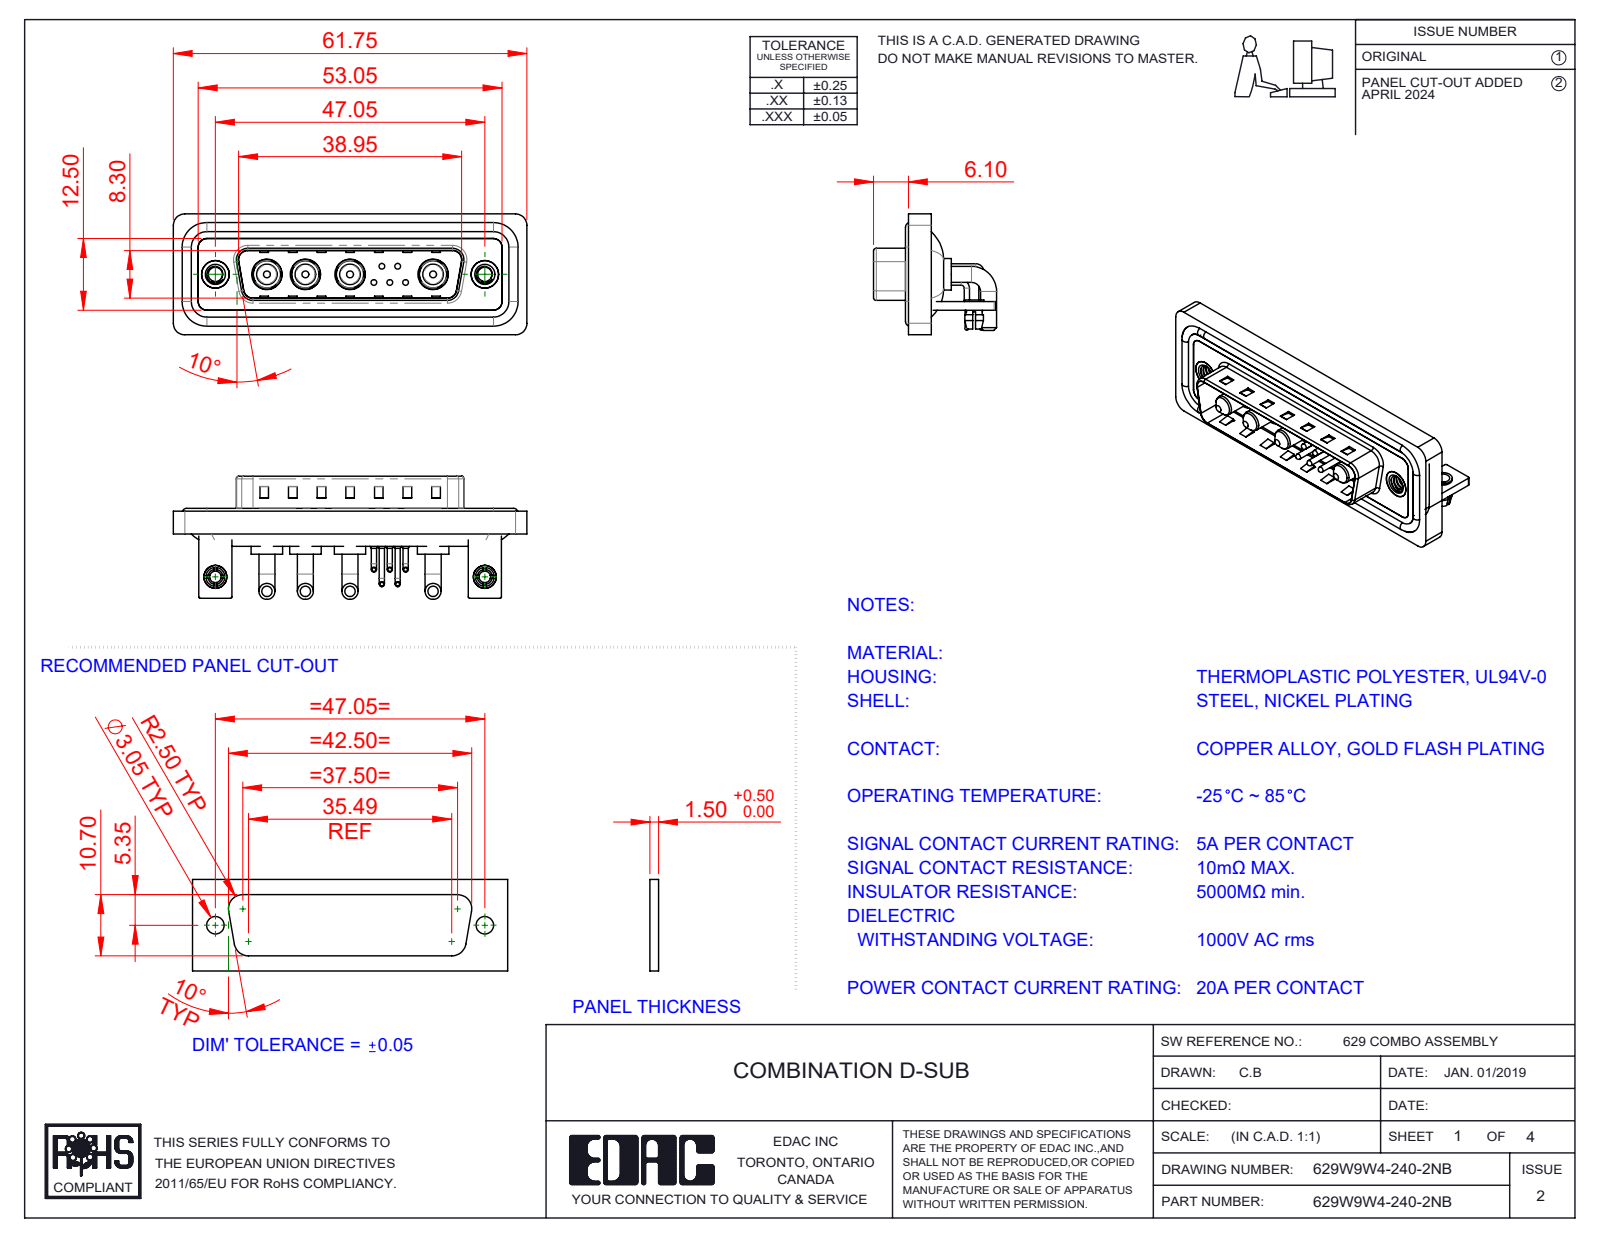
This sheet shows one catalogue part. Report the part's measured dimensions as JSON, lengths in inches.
{"part_name": "629Combo Board Lock; 629Combo Stabilizer Bracket; Power Pin_20A RA; 629Combo Contact Row 1 (+7 more)", "step_written_by": "SolidWorks 2023 (CONFIG_CONTROL_DESIGN)", "units": "inches", "bodies": {"solids": 24, "faces": 1335, "planar": 637, "cylindrical": 502, "other": 196}, "overall_size": [2.431, 0.846, 0.831], "volume_in3": 0.489, "surface_area_in2": 20.42, "round_holes": [[0.079, 7], [0.03, 5], [0.063, 5], [0.098, 4], [0.191, 4], [0.209, 4], [0.126, 2], [0.157, 2], [0.189, 2], [0.197, 2]], "round_bosses_or_shafts": [[0.035, 10], [0.11, 8], [0.059, 5], [0.039, 5], [0.026, 5], [0.217, 4], [0.205, 4], [0.187, 4]], "partial_cylinders_radius": [[0.079, 19], [0.059, 18], [0.01, 16], [0.02, 9], [0.063, 8], [0.04, 5], [0.024, 4], [0.026, 4]], "face_to_face_distances": [0.016, 0.059, 0.031, 0.114, 0.083, 0.043, 0.146, 0.161, 0.177, 0.063], "hole_center_spacings": [0.124, 0.109, 0.198, 0.571, 1.852, 0.109, 0.173, 0.174]}
